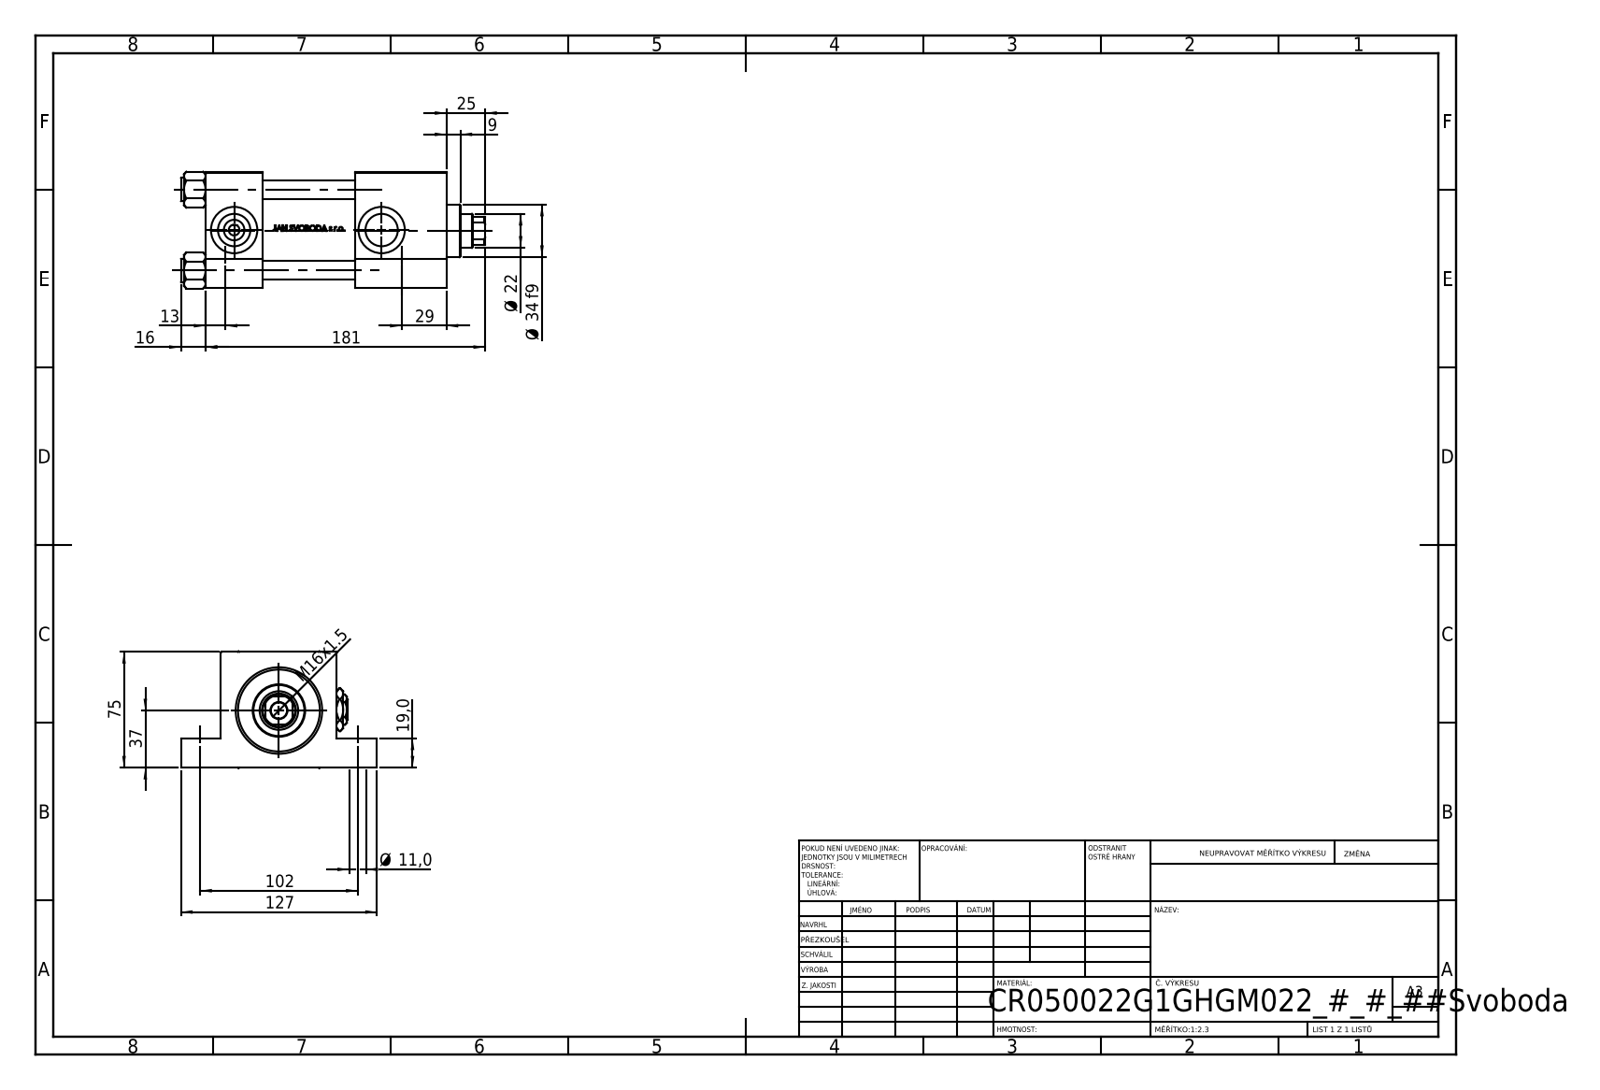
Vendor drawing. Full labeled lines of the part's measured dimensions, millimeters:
Part name (STEP PRODUCT): V215_VC_A; NUT_M5_G; Zatka_pro_OIL_PORT; V215CR_VCP_G (+2 more)
STEP written by: SolidWorks 2019 (CONFIG_CONTROL_DESIGN)
Units: millimetres
Bodies: 12 solids, 1134 faces (454 planar, 128 cylindrical, 552 other)
Overall size (bounding box): 197 × 127 × 75.54
Volume: 755 067 mm³ · Surface area: 162 409 mm²
Round holes (diameter × count): ⌀11 ×4, ⌀12 ×4, ⌀7 ×2, ⌀20.96 ×2, ⌀30 ×2, ⌀10.5 ×1, ⌀22 ×1, ⌀25 ×1, ⌀41 ×1, ⌀50 ×1, ⌀53 ×1
Round bosses / shafts (diameter × count): ⌀15 ×4, ⌀56 ×1, ⌀34 ×1
Partial cylindrical surfaces — rounded edges, fillets, slot ends (radius × count): R10.5 ×1
Main face-to-face distances: 75, 37, 156, 119, 19, 56, 97, 60, 59, 26
Hole centre spacings: 52.3, 36.63, 37.34, 73.96, 102, 114, 152.97, 95.5
